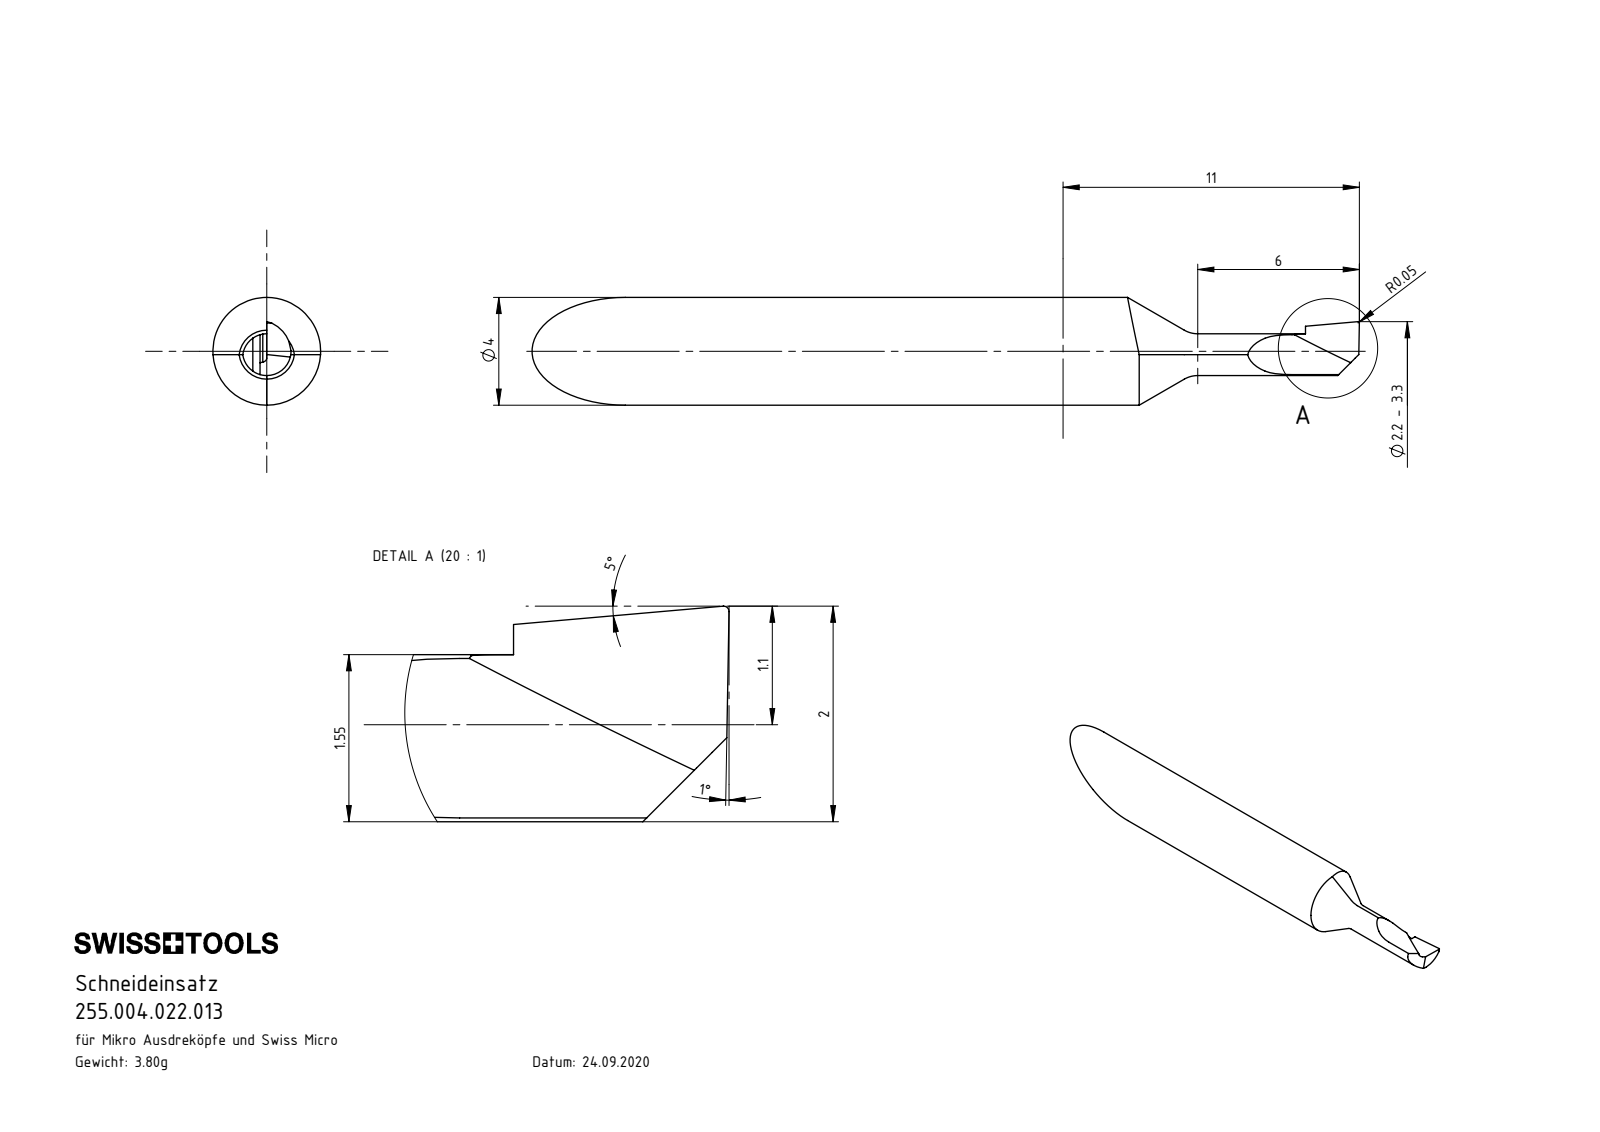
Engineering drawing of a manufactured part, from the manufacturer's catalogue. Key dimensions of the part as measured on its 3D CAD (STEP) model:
Part name (STEP PRODUCT): A04.0095.06.22.05_YR
STEP written by: SolidWorks 2017 (AUTOMOTIVE_DESIGN)
Units: millimetres
Bodies: 1 solid, 27 faces (8 planar, 6 cylindrical, 13 other)
Overall size (bounding box): 30.71 × 4 × 4
Volume: 262 mm³ · Surface area: 316 mm²
Round bosses / shafts (diameter × count): ⌀4 ×1
Partial cylindrical surfaces — rounded edges, fillets, slot ends (radius × count): R0.9 ×2, R2 ×1
Main face-to-face distances: 12.33
